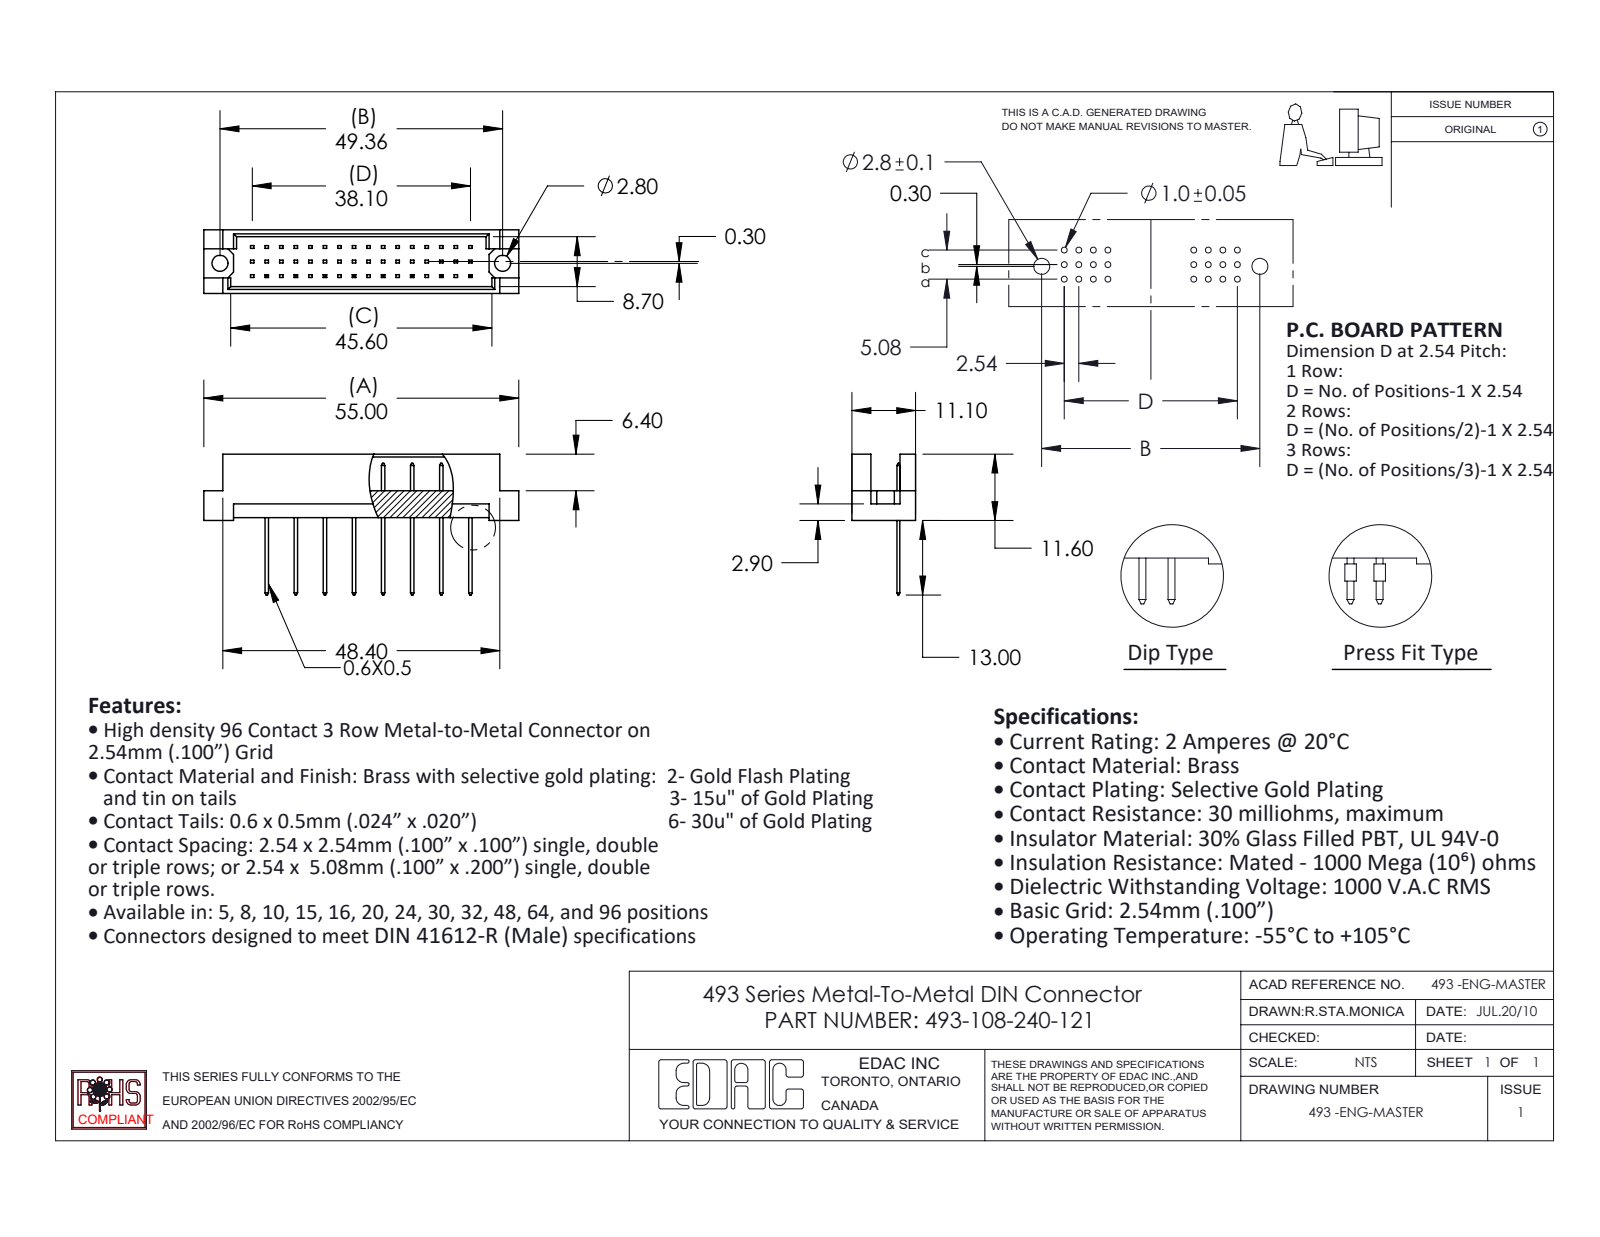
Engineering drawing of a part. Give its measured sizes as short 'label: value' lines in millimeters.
name: 493-108-240-121; 493-290_40; 493 Part_48
written by: SolidWorks 2020 (CONFIG_CONTROL_DESIGN)
unit: mm
bodies: 9 solids, 356 faces (352 planar, 4 cylindrical, 0 other)
size: 55 × 24.6 × 11.1
volume: 3 327 mm³; area: 4 158 mm²
holes: 2× ⌀2.8
face distances: 1.2, 9.9, 11.1, 8.7, 4.7, 0.5, 5.08, 2.76, 8.34, 1.56
hole spacings: 49.36
